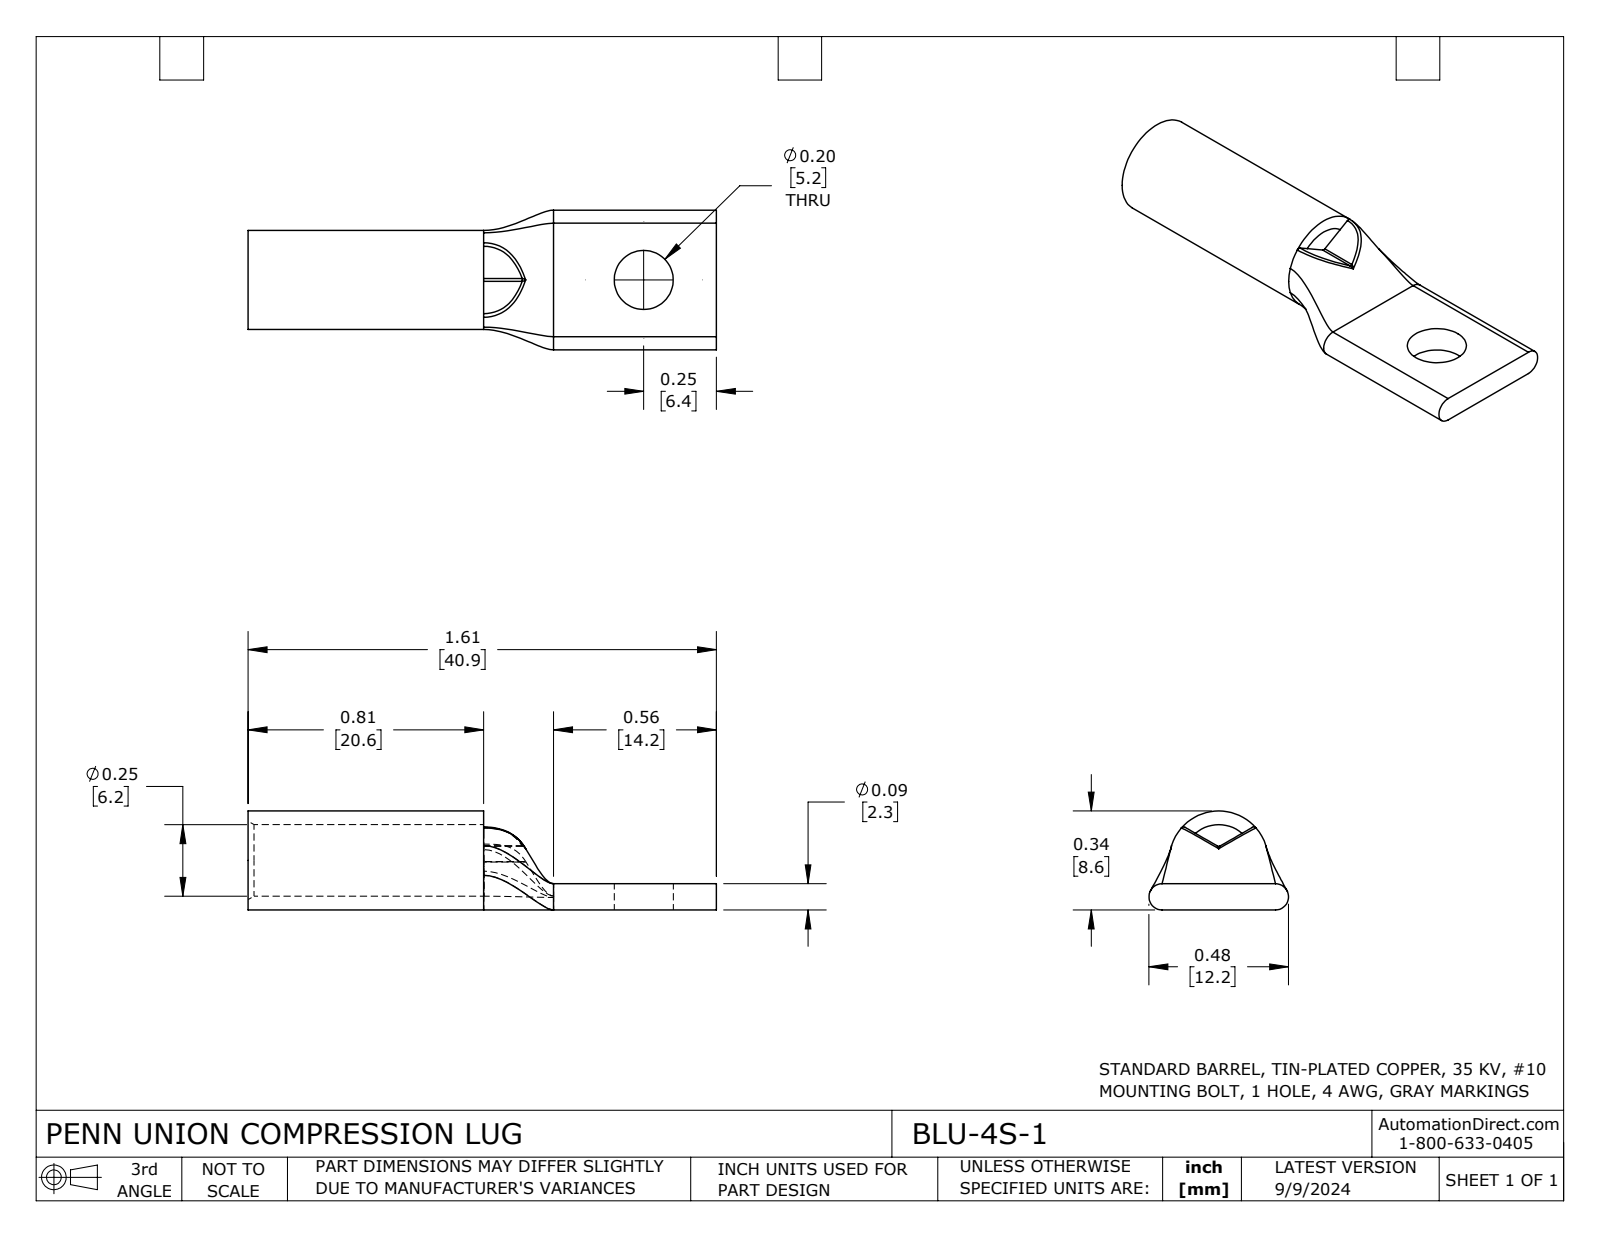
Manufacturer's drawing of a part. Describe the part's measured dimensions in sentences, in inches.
The part is named "BLU-4S-1". Its 3-D file was written by "SolidWorks 2023 (CONFIG_CONTROL_DESIGN)". It is 1 solid with 35 faces: 11 planar, 11 cylindrical and 13 other. Overall it measures 1.61 by 0.48 by 0.34 inches. Its volume is 0.065 cubic inches and its surface area 2.667 square inches. Round holes: 1 of diameter 0.203, 1 of diameter 0.246. Round bosses or shafts: 1 of diameter 0.34. Partial cylindrical surfaces (rounded edges, fillets, slot ends): 2 of radius 0.01, 2 of radius 0.045. The main face-to-face distances are 0.09, 1.61, 0.047, 0.81, 0.8, 1.05, 0.24, 0.56.
